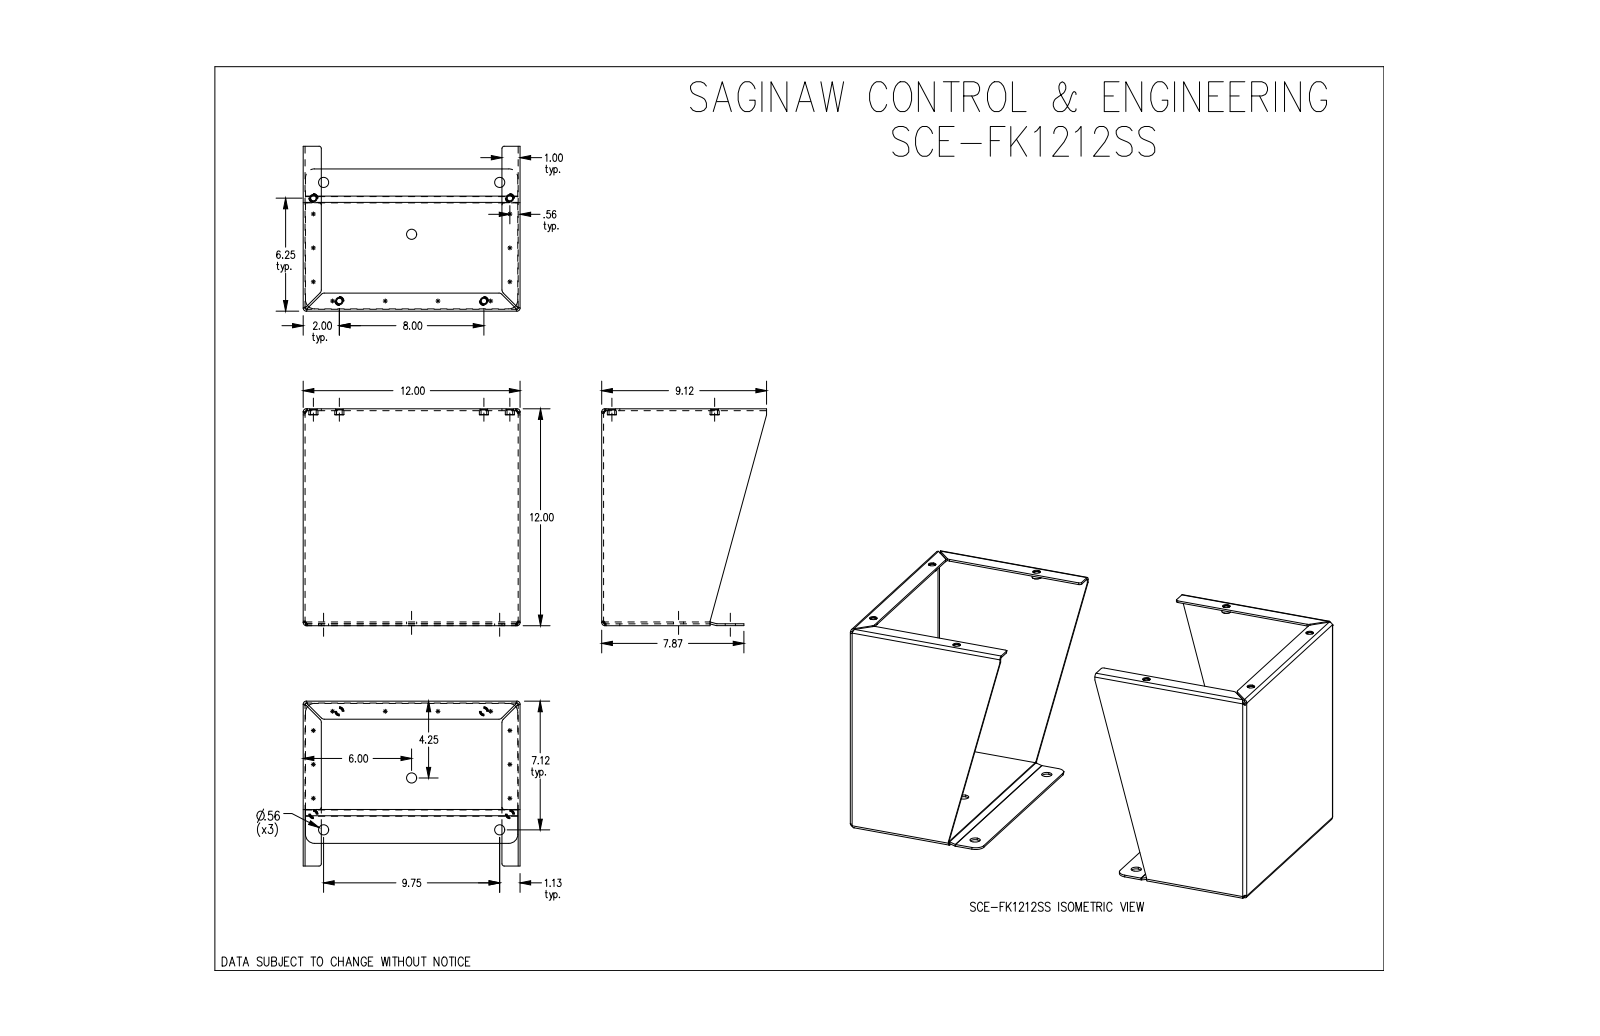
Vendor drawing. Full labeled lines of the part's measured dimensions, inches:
Part name (STEP PRODUCT): SCE-FK1212SS
STEP written by: SolidWorks 2019 (CONFIG_CONTROL_DESIGN)
Units: inches
Bodies: 12 solids, 286 faces (120 planar, 110 cylindrical, 56 other)
Overall size (bounding box): 24 × 12 × 12
Volume: 94.47 in³ · Surface area: 1 847 in²
Round holes (diameter × count): ⌀0.312 ×8, ⌀0.413 ×8, ⌀0.563 ×6
Round bosses / shafts (diameter × count): ⌀0.5 ×8, ⌀0.412 ×8
Partial cylindrical surfaces — rounded edges, fillets, slot ends (radius × count): R0.166 ×16, R0.062 ×12, R0.125 ×8, R0.22 ×8, R0.5 ×8, R0.063 ×4
Main face-to-face distances: 0.104, 11.896, 23.896, 11.792, 12, 24, 23.792, 0.101, 11.893, 11.688
Hole centre spacings: 1.035, 5.441, 5.656, 5.793, 5.866, 6.614, 10.646, 11.019
